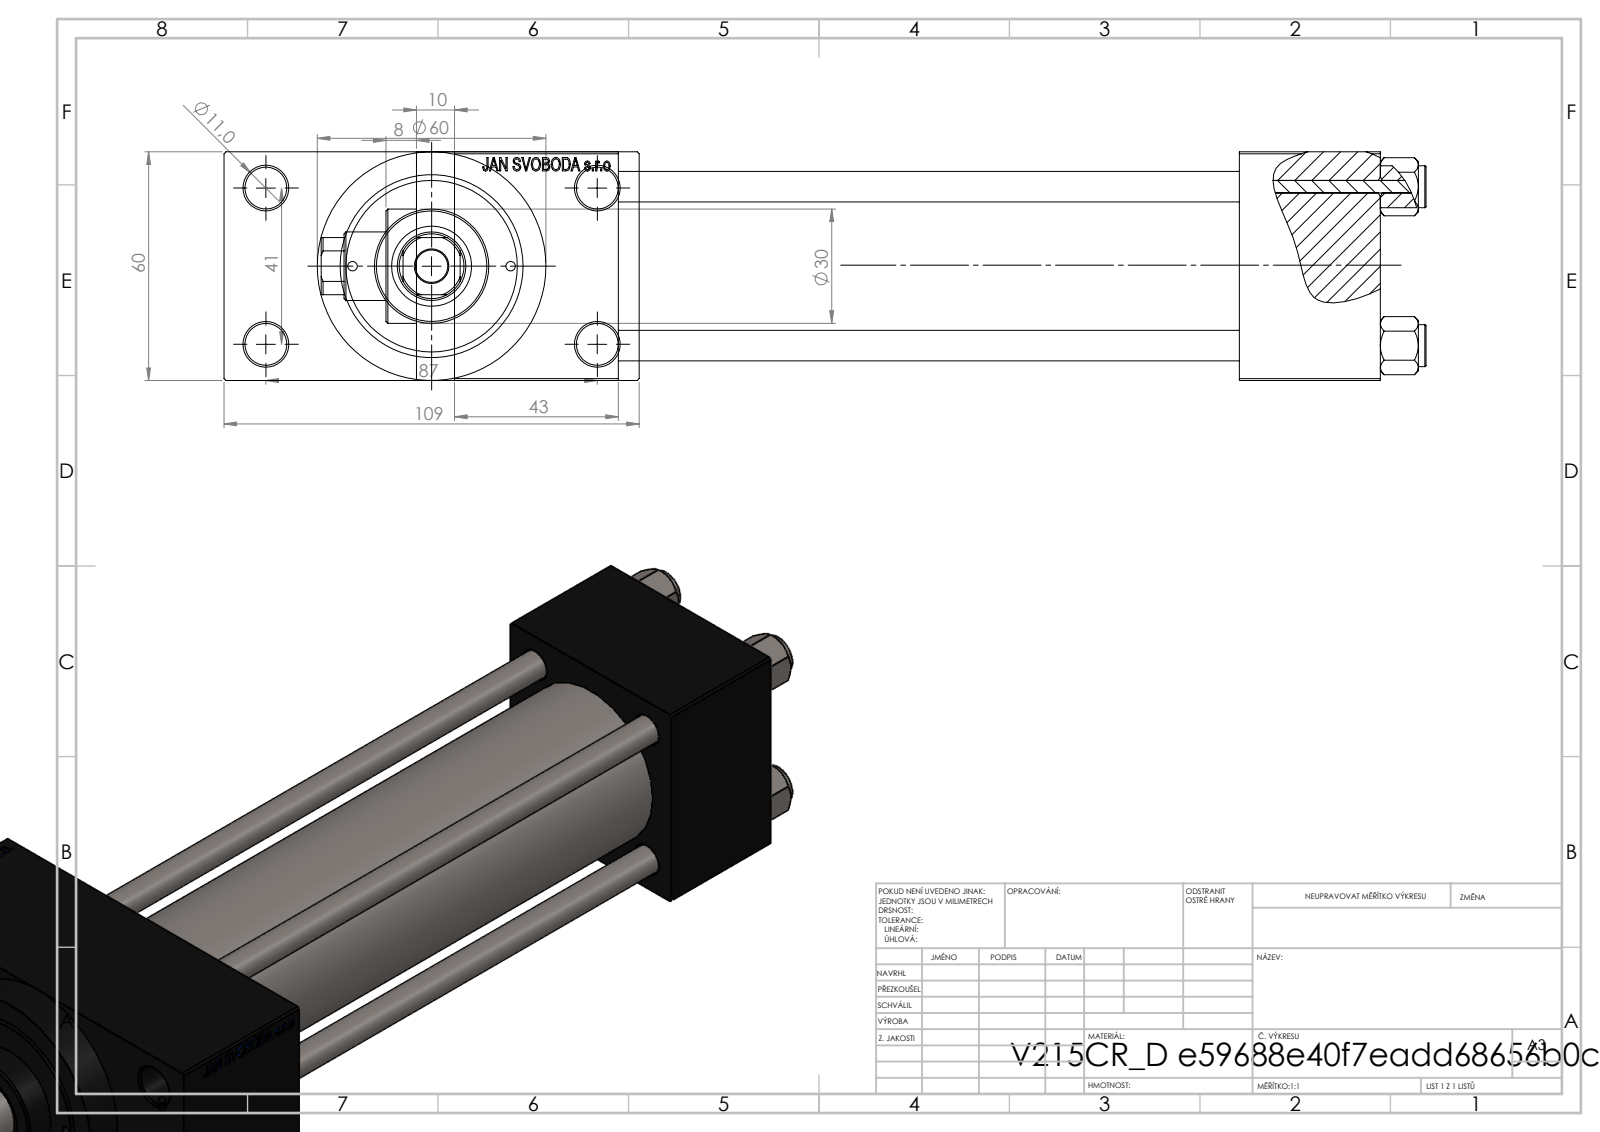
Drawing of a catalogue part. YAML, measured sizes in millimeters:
part_name: "V215CR_D_Body; V215CR_D_TYCINKA; NUT_M5_D; V215_VC_A (+1 more)"
step_written_by: "SolidWorks 2019 (CONFIG_CONTROL_DESIGN)"
units: millimeters
bodies: {solids: 11, faces: 1112, planar: 500, cylindrical: 92, other: 520}
overall_size: [290, 109, 60]
volume: 602694
surface_area: 167366
round_holes:
  - {diameter: 8, count: 4}
  - {diameter: 11, count: 4}
  - {diameter: 2.5, count: 2}
  - {diameter: 7, count: 2}
  - {diameter: 16.66, count: 2}
  - {diameter: 24, count: 2}
  - {diameter: 8.5, count: 1}
  - {diameter: 18, count: 1}
  - {diameter: 21, count: 1}
  - {diameter: 31, count: 1}
  - {diameter: 40, count: 1}
  - {diameter: 45, count: 1}
round_bosses_or_shafts:
  - {diameter: 11, count: 4}
  - {diameter: 60, count: 1}
  - {diameter: 46, count: 1}
  - {diameter: 30, count: 1}
partial_cylinders:
  - {radius: 8.5, count: 1}
face_to_face_distances: [60, 163, 24.5, 84.5, 37, 200, 243, 206, 43, 209.74]
hole_center_spacings: [20.85, 22.65, 29.49, 30.62, 41.7, 46.53, 47.15, 48.09]
